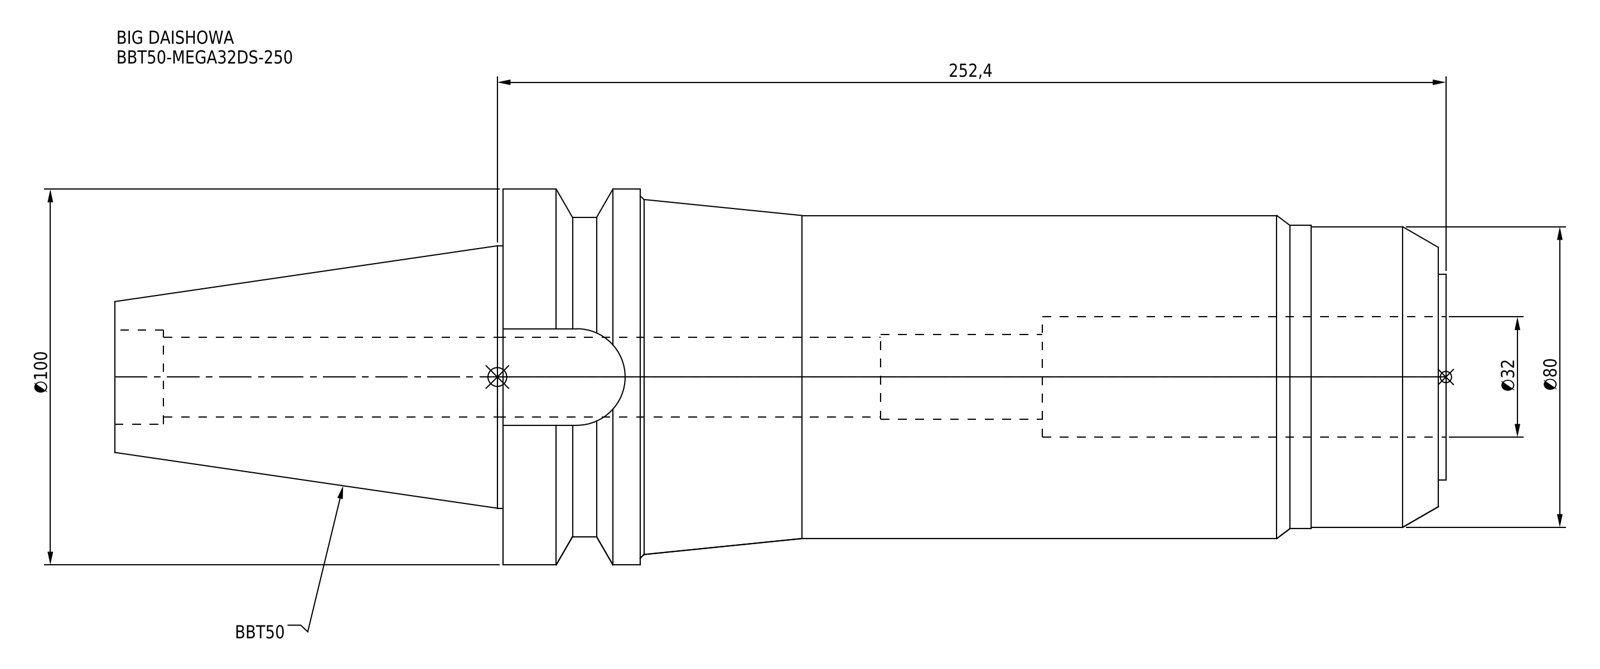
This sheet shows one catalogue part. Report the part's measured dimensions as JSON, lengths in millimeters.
{"part_name": "BBT50-MEGA32DS-250", "step_written_by": "CREO PARAMETRIC BY PTC INC, 2016380 (AUTOMOTIVE_DESIGN)", "units": "millimeters", "bodies": {"solids": 1, "faces": 57, "planar": 15, "cylindrical": 28, "other": 14}, "overall_size": [354.2, 100, 100], "volume_mm3": 1549000, "surface_area_mm2": 126888, "round_holes": [[21.2, 1], [22.5, 1], [25, 1], [32, 1]], "round_bosses_or_shafts": [[100, 1], [86, 1], [85, 1], [80.7, 1], [80, 1], [69.85, 1], [54.7, 1]], "partial_cylinders_radius": [[12.85, 1]], "face_to_face_distances": [250.9, 2, 248.9, 354.2, 352.2, 103.3, 70.8, 214.4, 212.4, 36.5]}
